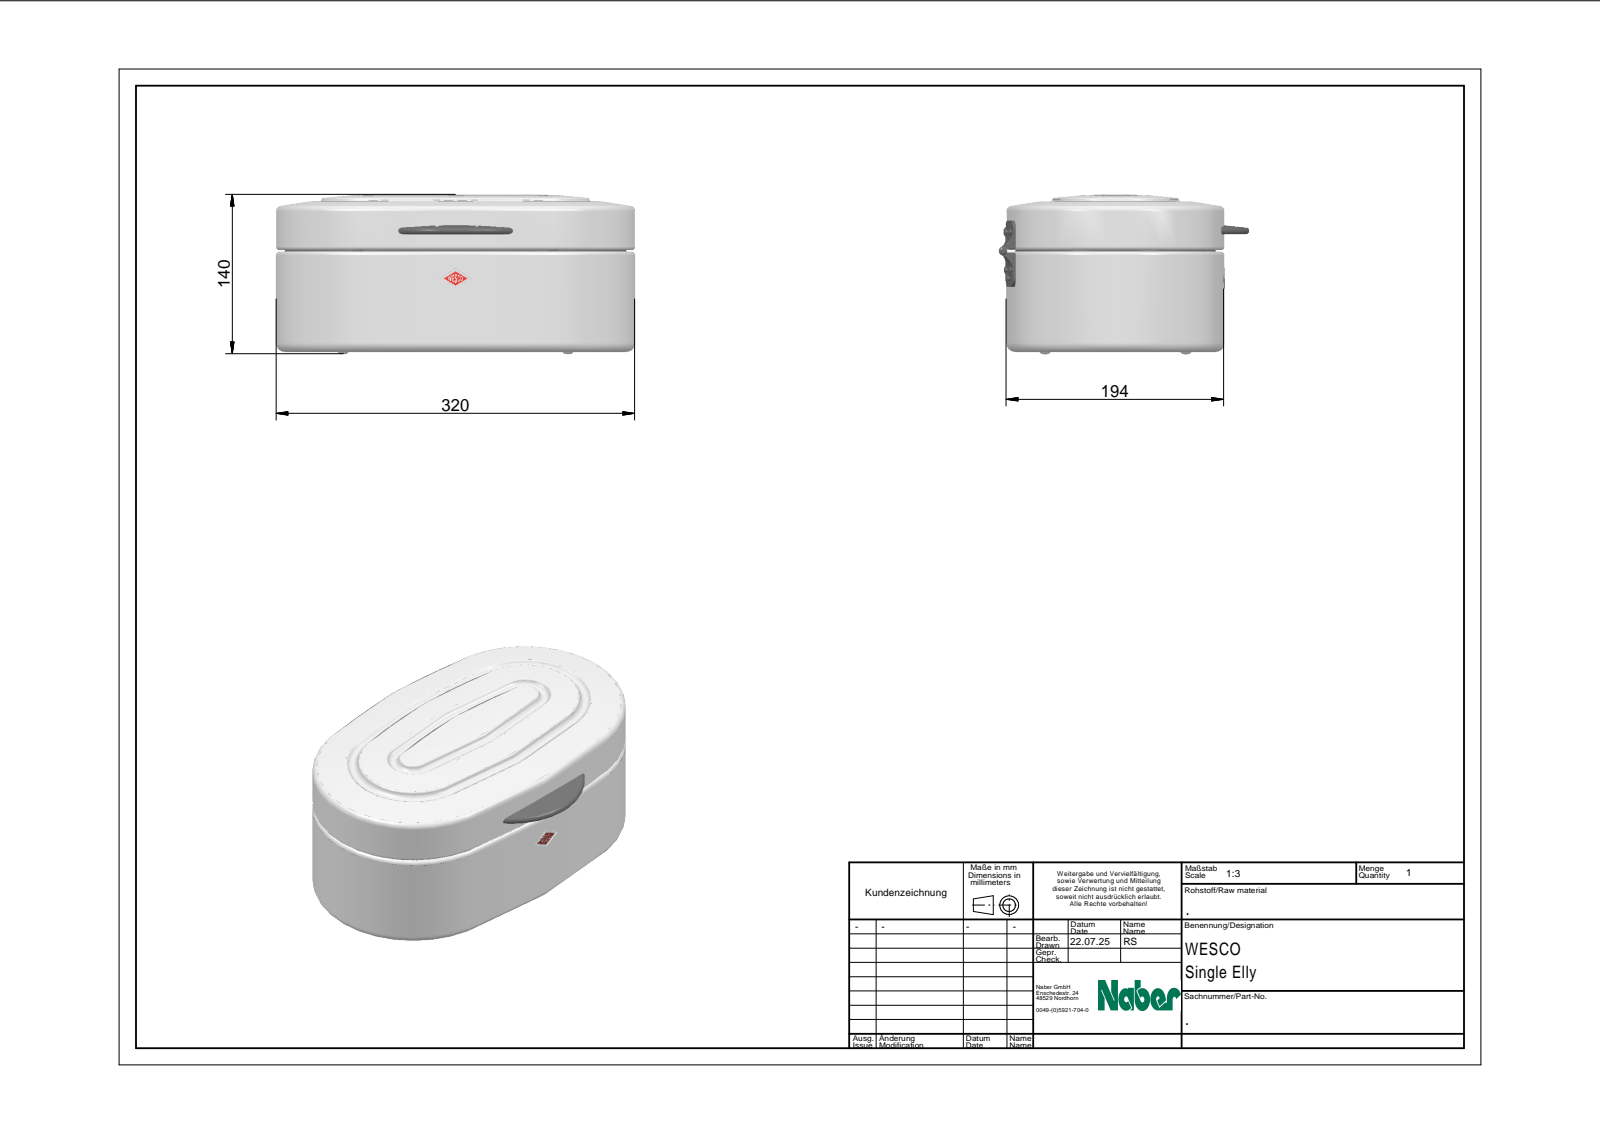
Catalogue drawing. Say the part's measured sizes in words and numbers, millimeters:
The part is named "0001_ASM|PRODUCT_293#PRODUCT_293;PRODUCT_293". Its 3-D file was written by "Spatial InterOp 3D (AUTOMOTIVE_DESIGN)". It is 5 solids with 2488 faces: 65 planar, 0 cylindrical and 2423 other. Overall it measures 1578.25 by 900 by 296.62 millimeters. The main face-to-face distances are 0.61, 0.52, 0.69, 1.3, 1.15, 0.54, 1.13, 1.82, 0.47, 1.01.
